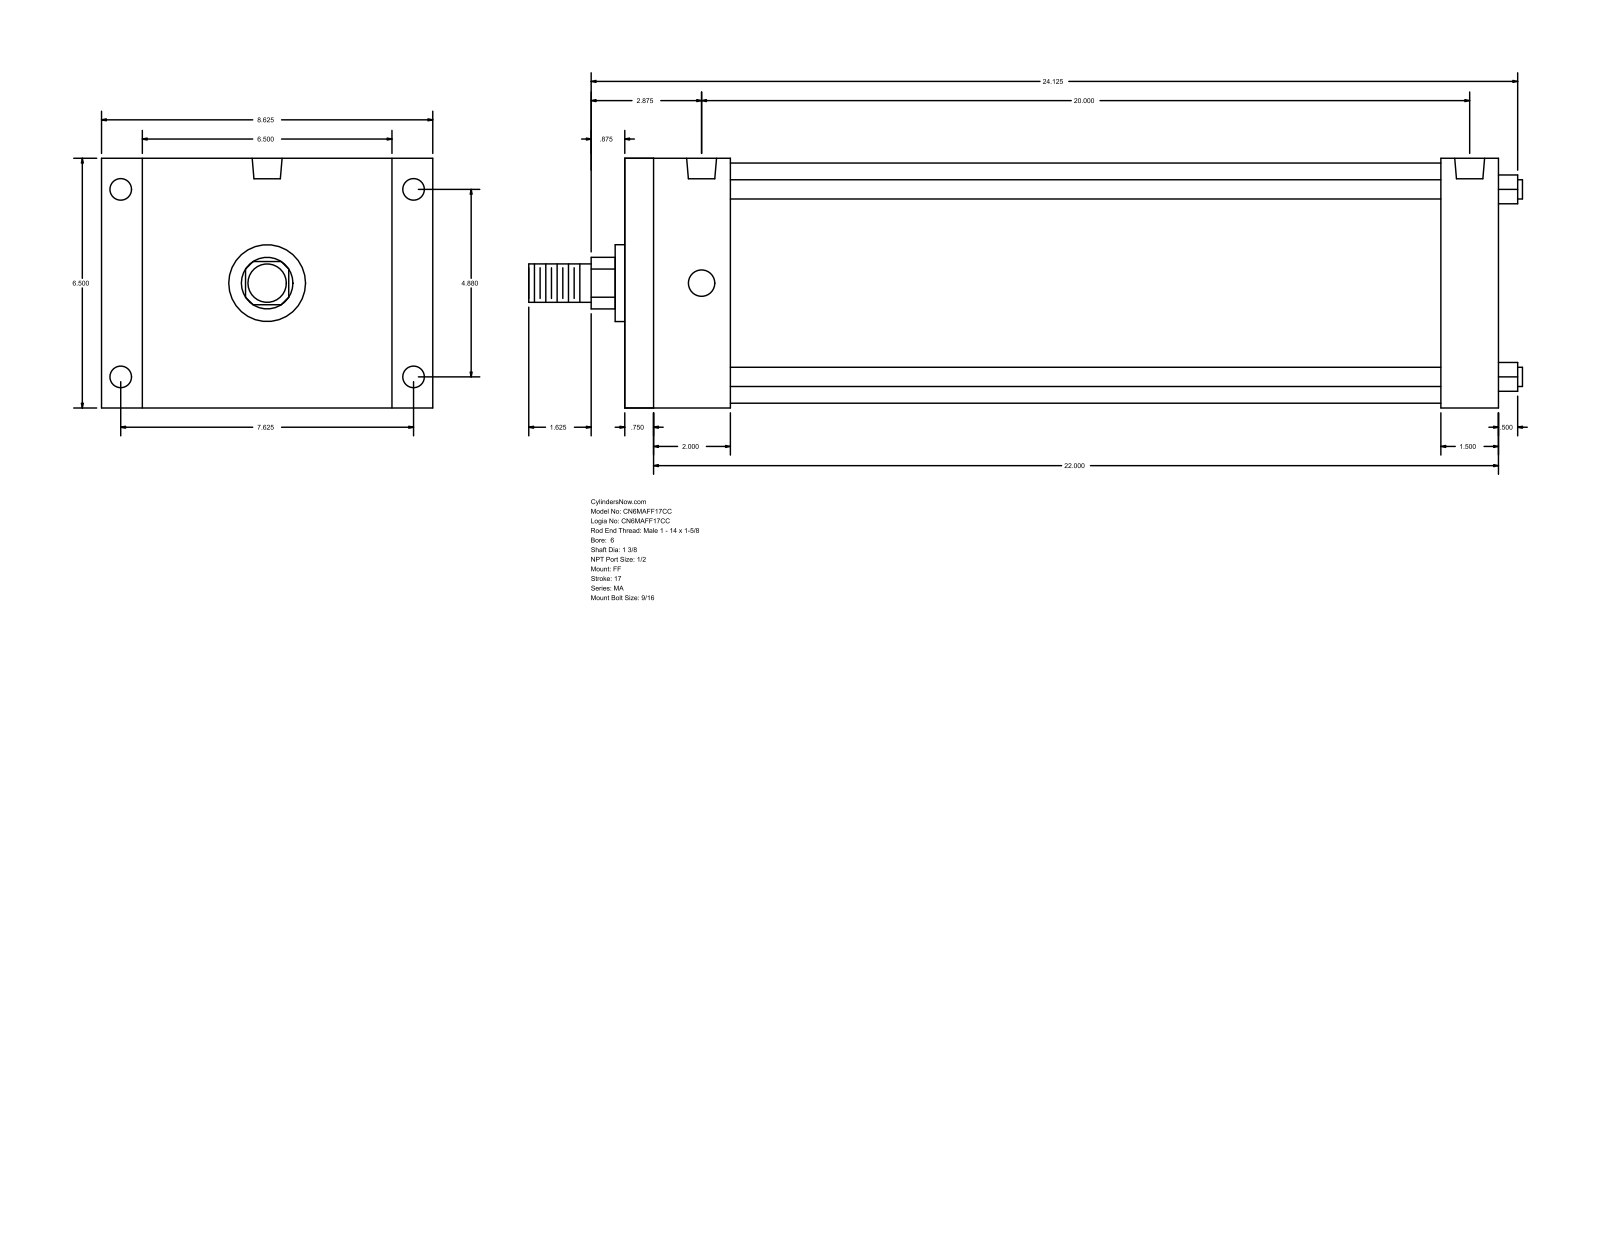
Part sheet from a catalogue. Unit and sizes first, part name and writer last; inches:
Units: inches
Overall size (bounding box): 25.875 × 8.625 × 6.5
Round holes (diameter × count): ⌀0.563 ×4, ⌀0.687 ×4, ⌀0.778 ×2
Round bosses / shafts (diameter × count): ⌀0.5 ×4, ⌀6.25 ×1, ⌀2 ×1, ⌀1.375 ×1, ⌀1 ×1
Partial cylindrical surfaces — rounded edges, fillets, slot ends (radius × count): R0.672 ×1
Main face-to-face distances: 6.5, 22.75, 0.625, 22.125, 1.5, 2.625, 2, 20.125, 21.25, 20.625
Hole centre spacings: 4.88, 7.625, 9.053, 20.125, 0.125, 20
Bodies: 0 solids, 92 faces (64 planar, 28 cylindrical, 0 other)
Part name (STEP PRODUCT): MA_FF__0600_1.375
STEP written by: GSSL Pune (CONFIG_CONTROL_DESIGN)
